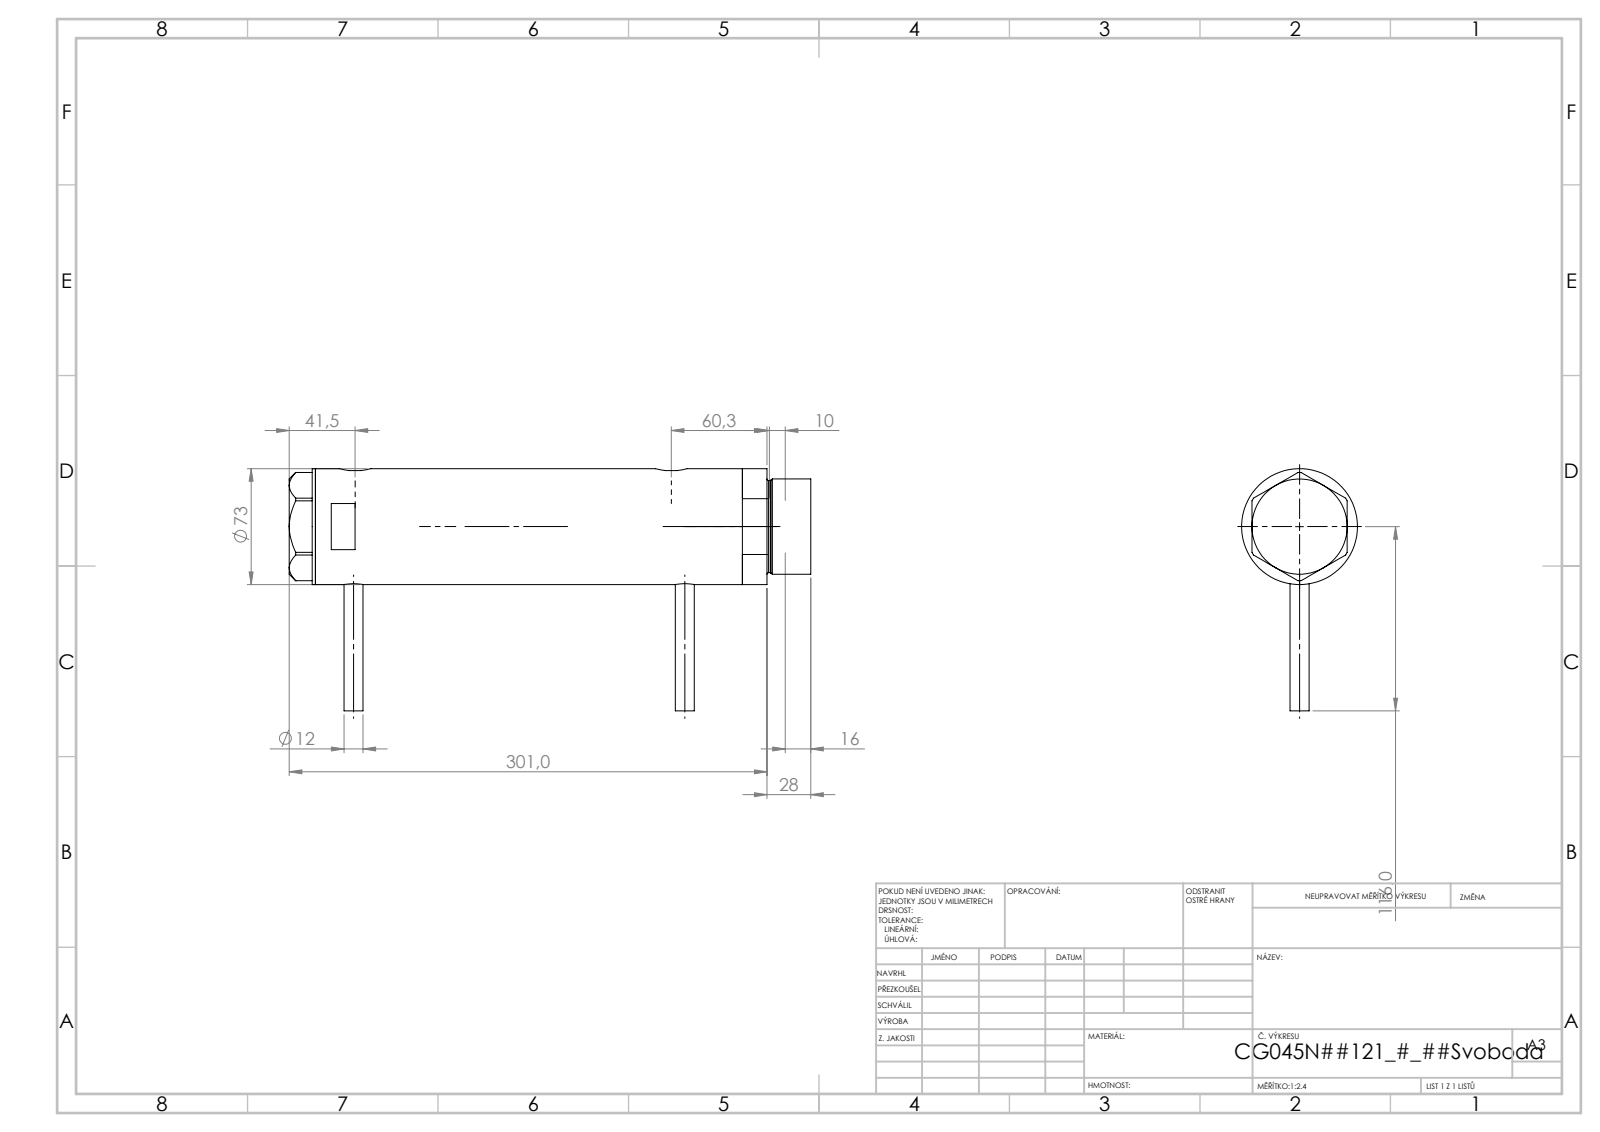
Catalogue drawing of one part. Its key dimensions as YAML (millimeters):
part_name: "V270CG_FRONT; V270CG_VC; V270CG_MIDDLE; V270CG_BACK"
step_written_by: "SolidWorks 2019 (CONFIG_CONTROL_DESIGN)"
units: millimeters
bodies: {solids: 4, faces: 125, planar: 50, cylindrical: 55, other: 20}
overall_size: [328.57, 152.5, 73]
volume: 1186000
surface_area: 198698
round_holes:
  - {diameter: 5, count: 2}
  - {diameter: 12.5, count: 2}
  - {diameter: 13.16, count: 2}
  - {diameter: 10.5, count: 1}
  - {diameter: 32, count: 1}
  - {diameter: 33.5, count: 1}
  - {diameter: 45, count: 1}
  - {diameter: 48, count: 1}
  - {diameter: 64, count: 1}
round_bosses_or_shafts:
  - {diameter: 12, count: 2}
  - {diameter: 73, count: 1}
  - {diameter: 60, count: 1}
  - {diameter: 58, count: 1}
  - {diameter: 31, count: 1}
partial_cylinders:
  - {radius: 10, count: 2}
face_to_face_distances: [224.2, 26, 198.2, 16.5, 42.5, 240.7, 2, 312.07, 328.57, 286.07]
hole_center_spacings: [1, 8.5, 199.2, 200.2, 207.7, 208.7]
